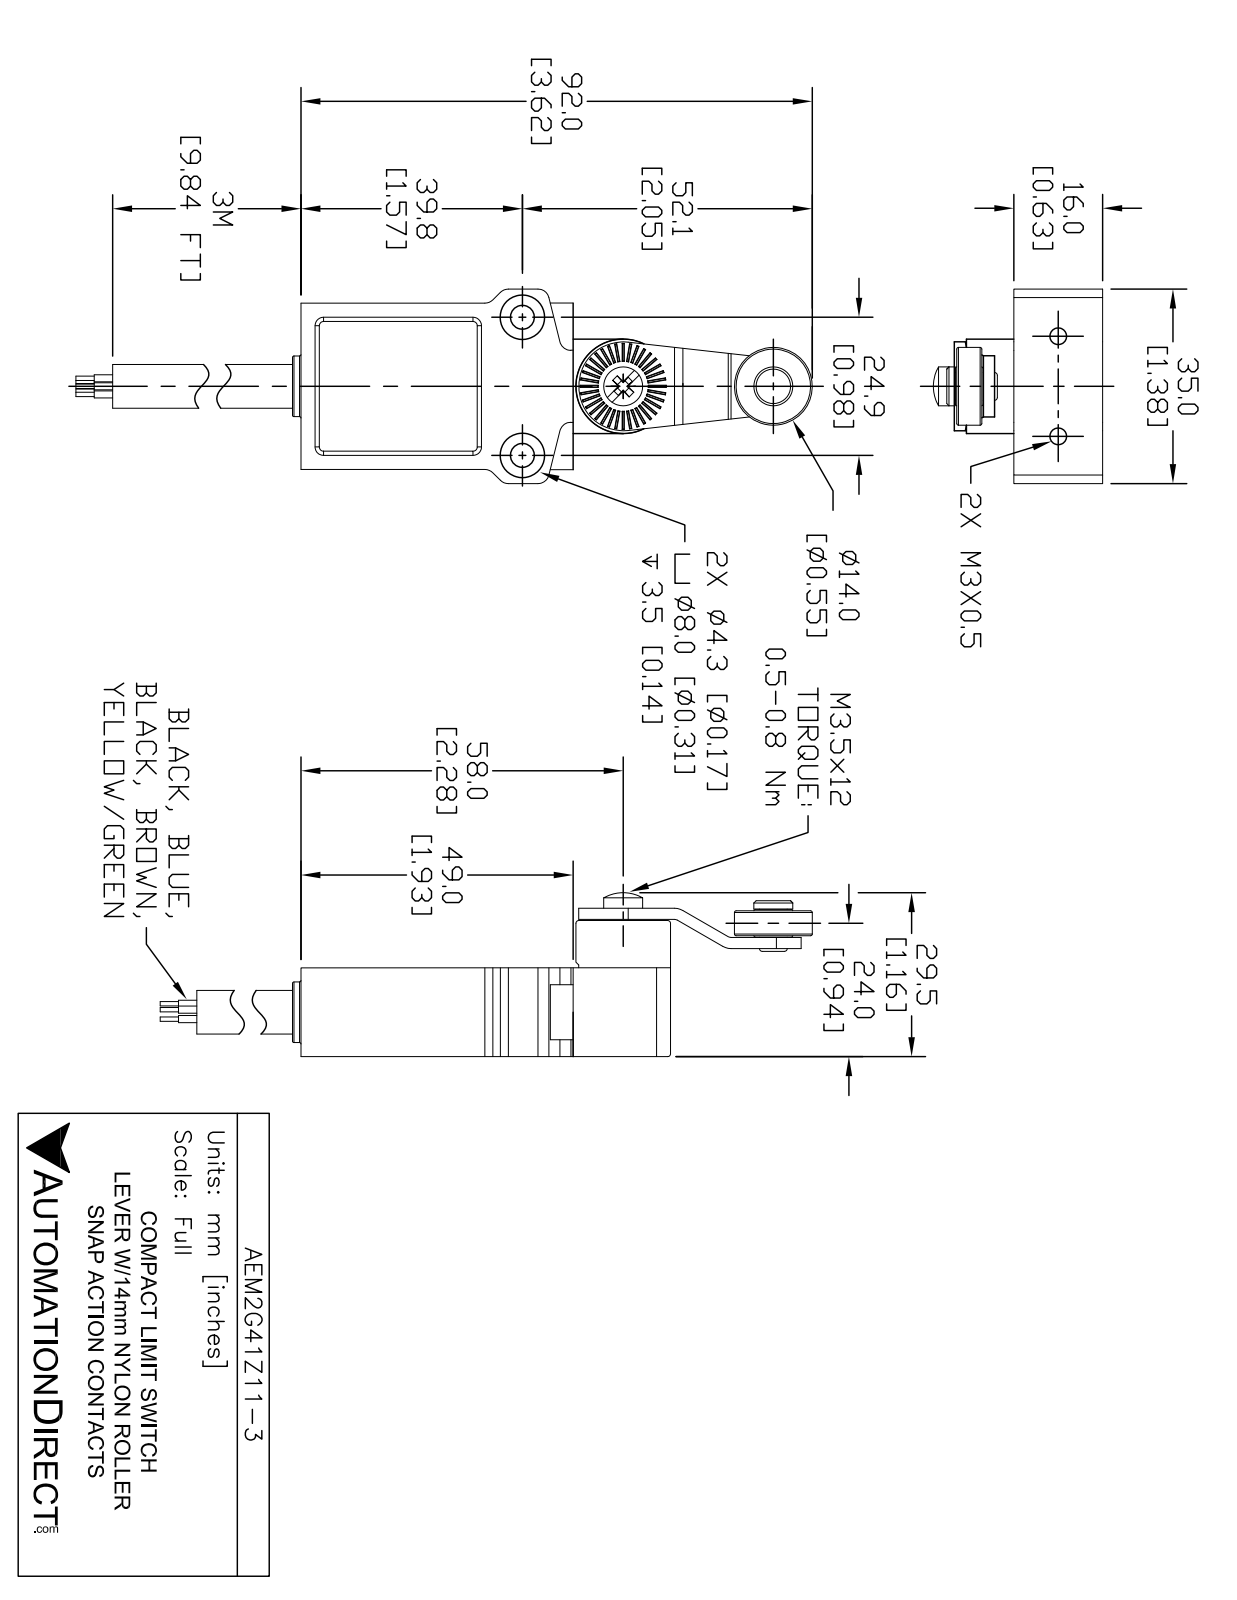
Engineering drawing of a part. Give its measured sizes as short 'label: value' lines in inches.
name: AEM2G41Z11-3_Default
written by: SolidWorks 2021 (CONFIG_CONTROL_DESIGN)
unit: in
bodies: 4 solids, 319 faces (249 planar, 55 cylindrical, 15 other)
size: 4.124 × 1.378 × 1.184
volume: 1.836 in³; area: 16.57 in²
holes: 2× ⌀0.118, 2× ⌀0.173, 2× ⌀0.323, 1× ⌀0.163, 1× ⌀0.197
bosses: 2× ⌀0.276, 1× ⌀0.622, 1× ⌀0.55, 1× ⌀0.28, 1× ⌀0.202, 1× ⌀0.143
rounds: 8× R0.079, 2× R0.06, 1× R0.14, 1× R0.192, 1× R0.256, 1× R0.313
face distances: 0.63, 1.181, 1.929, 0.354, 0.08, 0.984, 0.121, 0.28, 0.902, 0.472
hole spacings: 0.863, 0.748, 0.984
